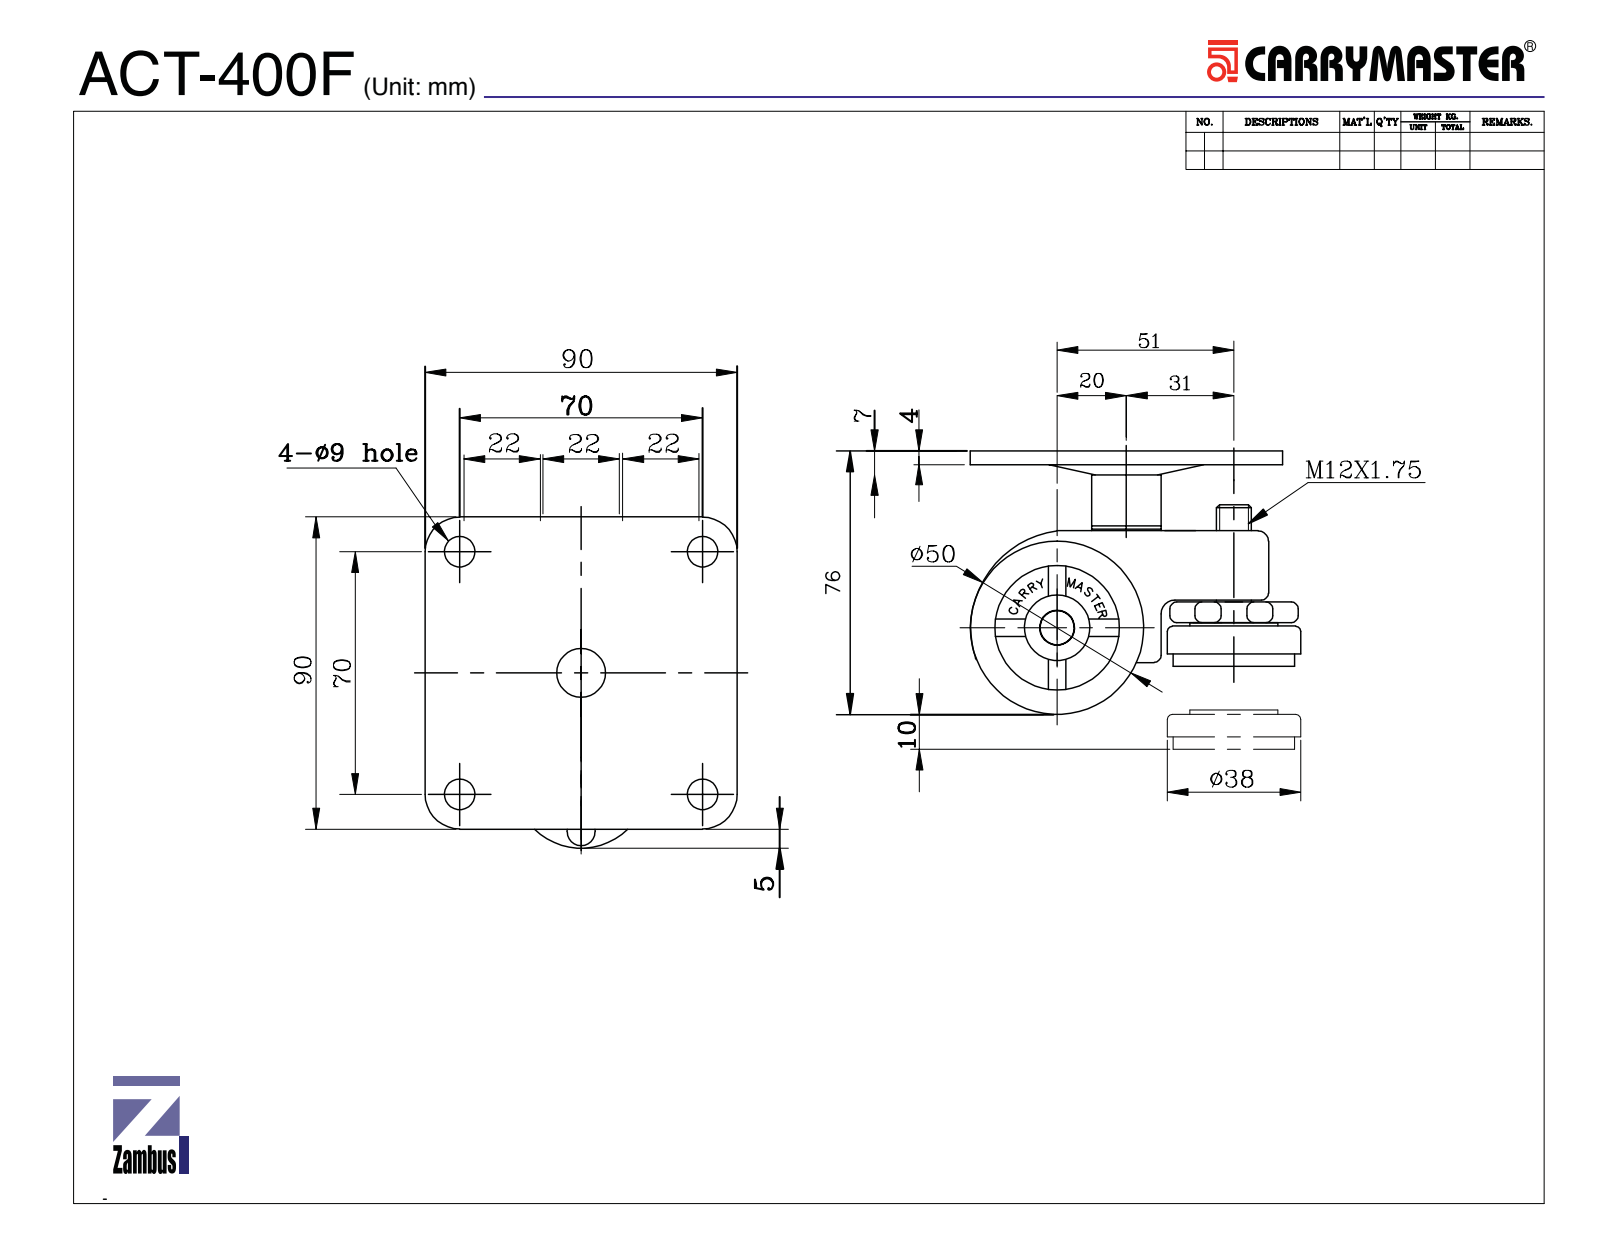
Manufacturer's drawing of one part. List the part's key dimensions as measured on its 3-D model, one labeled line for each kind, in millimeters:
Part name (STEP PRODUCT): ACT-400F
STEP written by: SolidWorks 2015 (CONFIG_CONTROL_DESIGN)
Units: millimetres
Bodies: 12 solids, 571 faces (223 planar, 150 cylindrical, 198 other)
Overall size (bounding box): 95.25 × 90 × 82.49
Volume: 178 157 mm³ · Surface area: 67 935 mm²
Round holes (diameter × count): ⌀9 ×4, ⌀10.2 ×2, ⌀2.2 ×1, ⌀5 ×1, ⌀6 ×1, ⌀6.5 ×1, ⌀7.5 ×1, ⌀10 ×1, ⌀13.2 ×1, ⌀14.1 ×1, ⌀14.5 ×1, ⌀15 ×1
Round bosses / shafts (diameter × count): ⌀20 ×2, ⌀38.5 ×1, ⌀35 ×1, ⌀19.8 ×1, ⌀19 ×1, ⌀16 ×1, ⌀15.2 ×1, ⌀14 ×1
Partial cylindrical surfaces — rounded edges, fillets, slot ends (radius × count): R5 ×16, R2 ×13, R4 ×7, R4.2 ×6, R10 ×4, R2.7 ×1, R3 ×1, R3.2 ×1
Main face-to-face distances: 4, 22, 45.7, 68.49, 72.49, 66.89, 22.75, 0.95, 1.6, 70.89
Hole centre spacings: 49.5, 70, 35.23, 74.71, 98.99, 16.35, 28, 31
